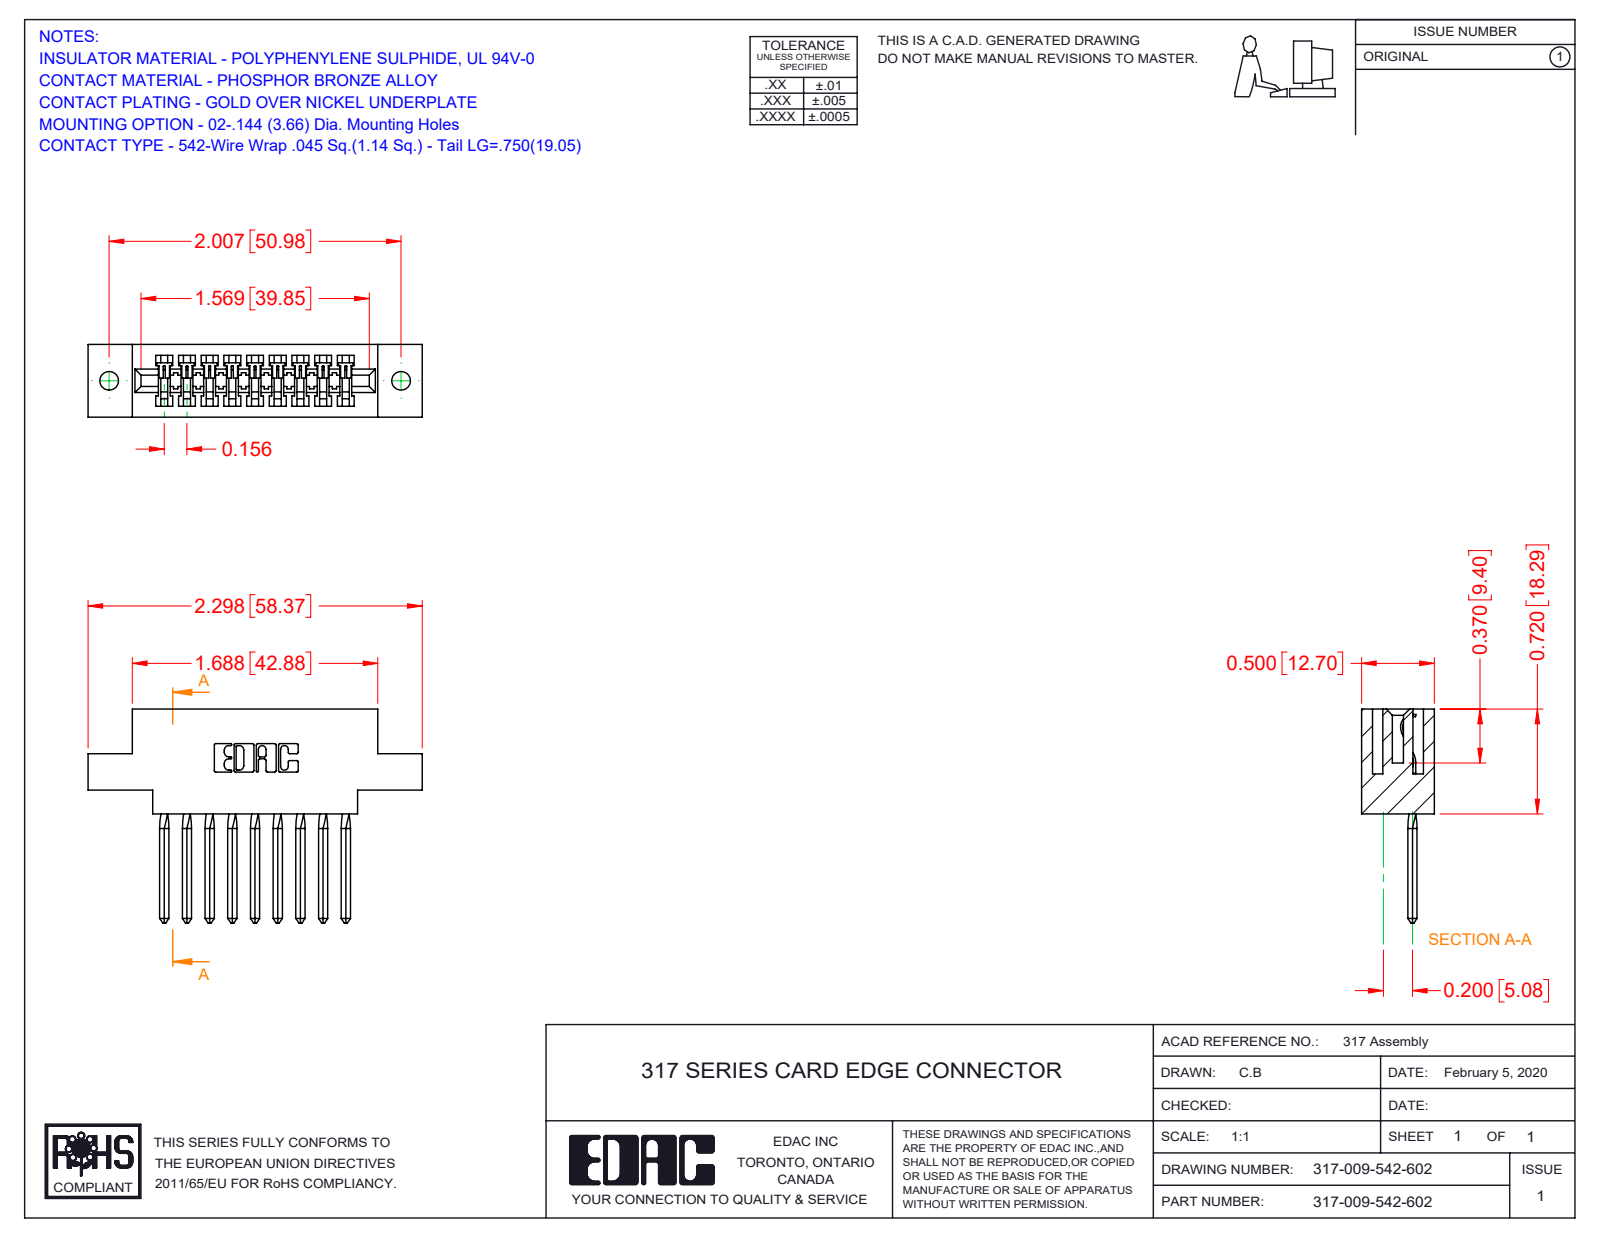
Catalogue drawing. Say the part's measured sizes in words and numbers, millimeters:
The part is named "317 Part_.144 Dia; 317-290-003_542; 317-009-542-602". Its 3-D file was written by "SolidWorks 2016 (CONFIG_CONTROL_DESIGN)". It is 10 solids with 777 faces: 634 planar, 107 cylindrical and 36 other. Overall it measures 58.4 by 37.3 by 12.7 millimeters. Its volume is 8 100 cubic millimeters and its surface area 8 871 square millimeters. Round holes: 2 of diameter 3.3. Partial cylindrical surfaces (rounded edges, fillets, slot ends): 22 of radius 0.3, 18 of radius 0.2, 6 of radius 0.2, 6 of radius 0.8, 3 of radius 0.7, 1 of radius 1.9, 1 of radius 2.3, 1 of radius 2.5. The main face-to-face distances are 12.7, 1.9, 10.8, 2.8, 1.7, 5.6, 4, 8.9, 2.9, 8.4. The hole center spacings are 51.
